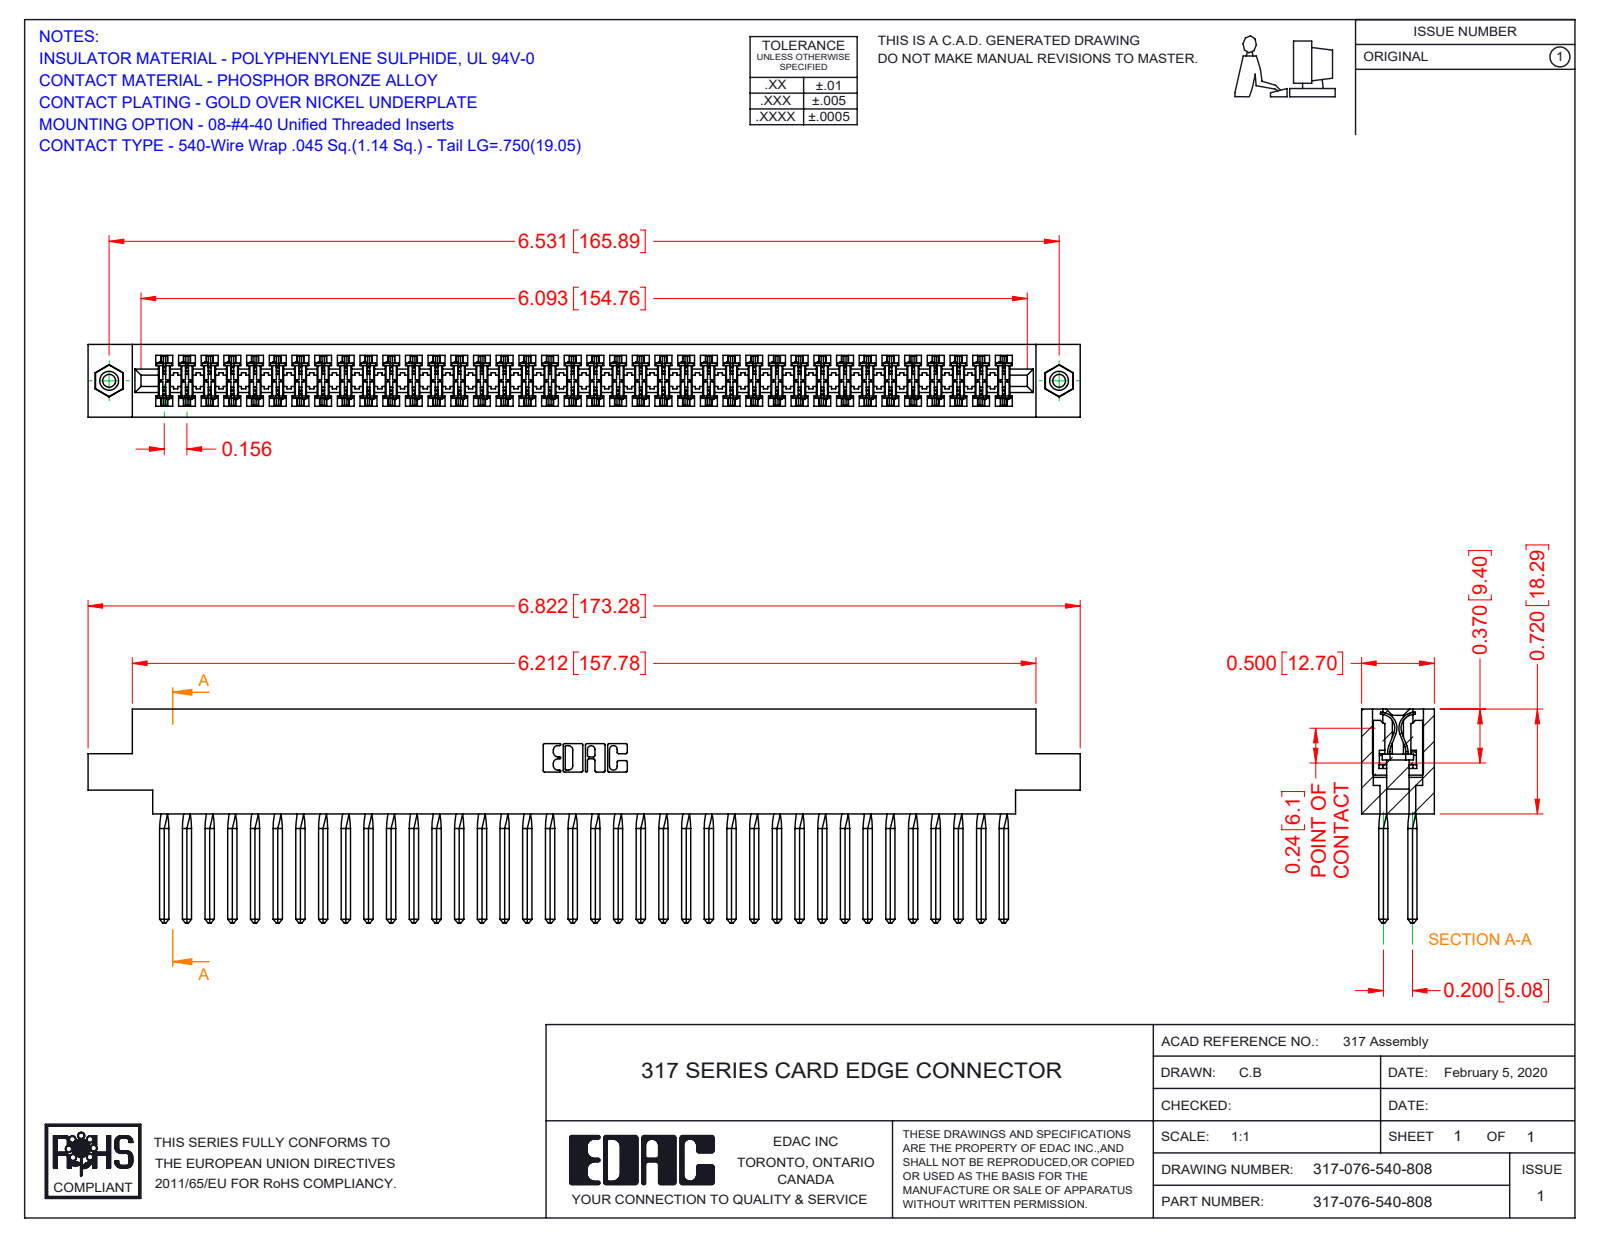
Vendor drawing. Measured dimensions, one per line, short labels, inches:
name: 317-076-540-808; 345-250-001_345-250-003-102; 317 Part_.156 Dia - TI; 317-290-001_540
written by: SolidWorks 2016 (CONFIG_CONTROL_DESIGN)
unit: in
bodies: 79 solids, 6926 faces (5638 planar, 968 cylindrical, 320 other)
size: 6.822 × 1.47 × 0.5
volume: 1.766 in³; area: 66.68 in²
holes: 2× ⌀0.089, 2× ⌀0.125, 2× ⌀0.156
bosses: 2× ⌀0.155
rounds: 152× R0.015, 22× R0.01, 6× R0.007, 6× R0.031, 3× R0.026, 2× R0.095, 2× R0.1, 2× R0.11
face distances: 0.5, 0.075, 0.425, 0.35, 0.195, 0.094, 0.11, 0.2, 0.115, 0.131
hole spacings: 6.531
